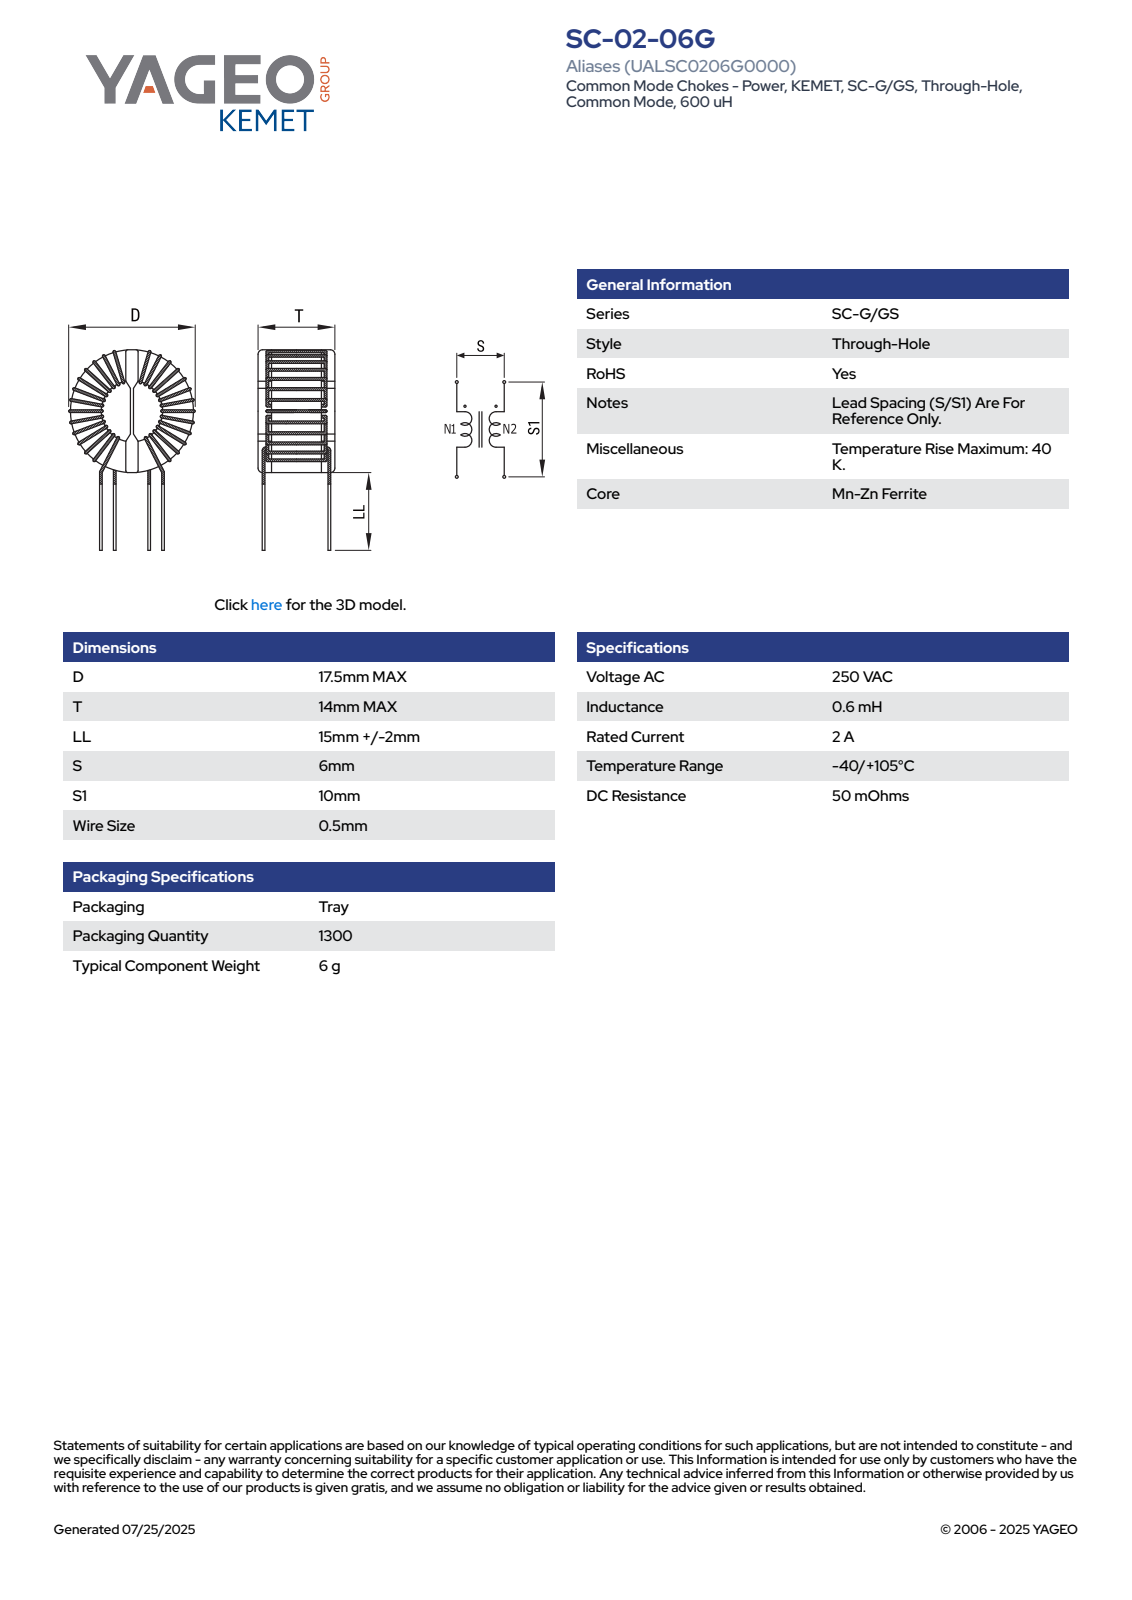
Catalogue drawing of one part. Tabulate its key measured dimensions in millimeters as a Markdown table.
| quantity | value |
| --- | --- |
| part name | SC-02-06G |
| STEP written by | SolidWorks 2018 (AUTOMOTIVE_DESIGN) |
| units | millimeters |
| bodies | 1 solid, 268 faces (121 planar, 65 cylindrical, 82 other) |
| overall size | 30.36 × 17.5 × 14 |
| volume | 1 791 mm³ |
| surface area | 1 733 mm² |
| round bosses / shafts (diameter × count) | 0.5 × 8 |
| partial cylindrical surfaces (radius × count) | 0.25 × 16, 2.32 × 1, 3.21 × 1, 3.62 × 1, 3.67 × 1, 3.8 × 1, 6.35 × 1, 6.4 × 1 |
| main face-to-face distances | 1.2, 2, 8.3, 0.8, 3.2, 2.85, 11.15, 1.15, 2.05, 0.85 |
